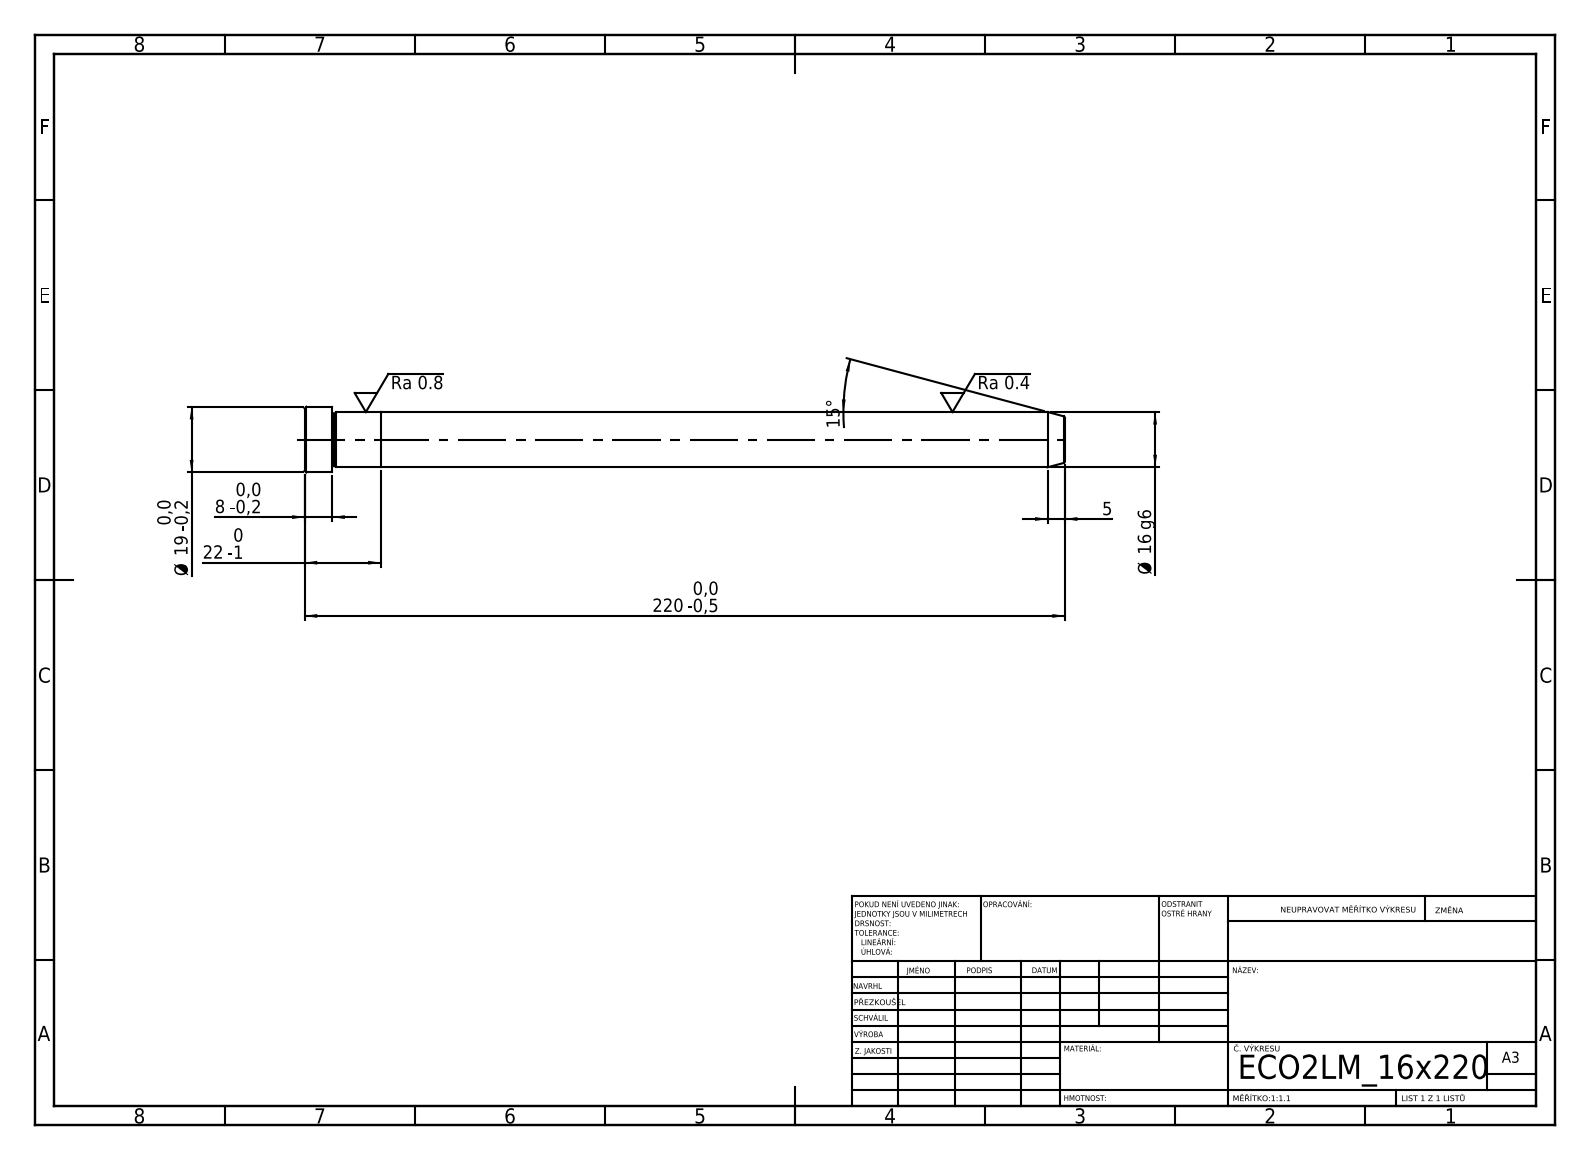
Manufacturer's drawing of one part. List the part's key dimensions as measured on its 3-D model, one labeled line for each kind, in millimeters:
STEP written by: SolidWorks 2019 (CONFIG_CONTROL_DESIGN)
Units: millimetres
Bodies: 2 solids, 21 faces (5 planar, 6 cylindrical, 10 other)
Overall size (bounding box): 220 × 19 × 19
Volume: 44 707 mm³ · Surface area: 12 031 mm²
Round bosses / shafts (diameter × count): ⌀19 ×1, ⌀16 ×1
Main face-to-face distances: 22, 198, 220, 212, 14, 8
